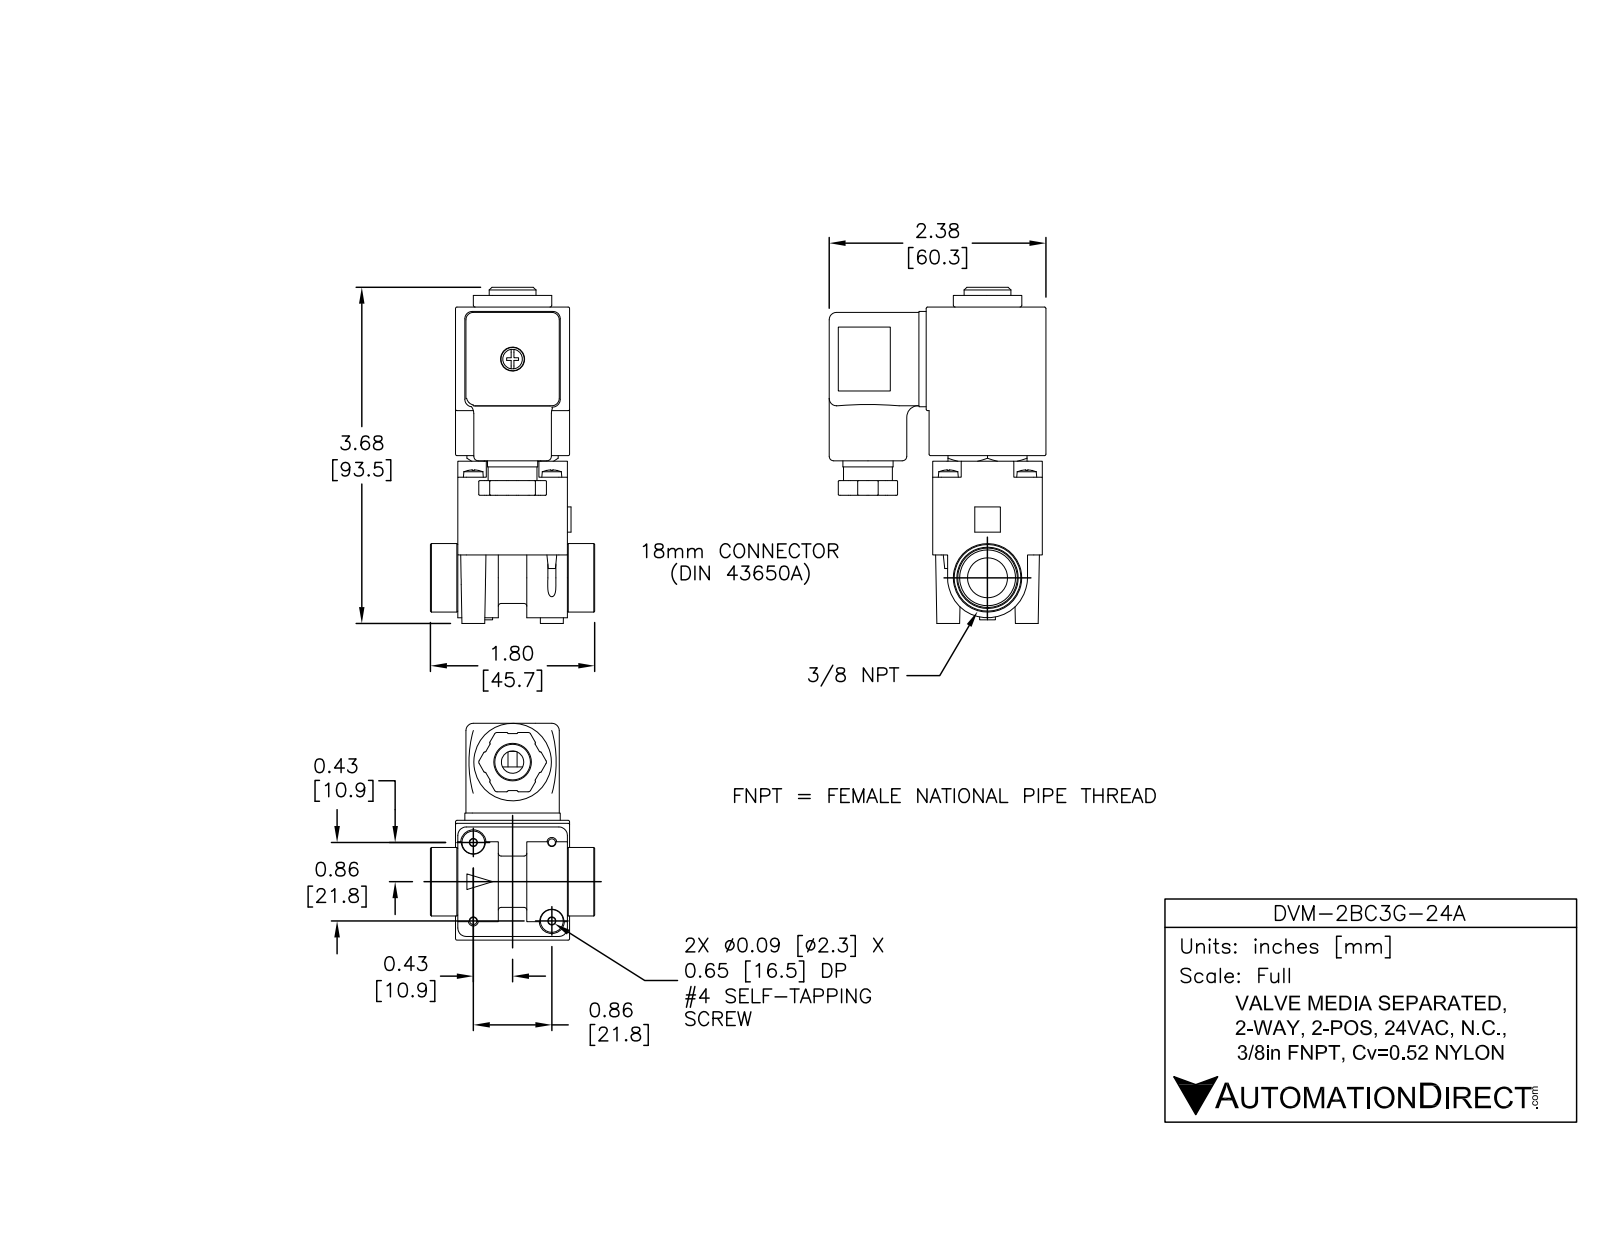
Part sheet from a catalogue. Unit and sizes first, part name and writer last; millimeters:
Units: millimetres
Overall size (bounding box): 93.5 × 60.3 × 45.7
Round holes (diameter × count): ⌀2.8 ×4, ⌀1.5 ×2, ⌀2.3 ×2, ⌀8 ×2, ⌀3 ×1, ⌀4 ×1, ⌀5.2 ×1, ⌀6.2 ×1, ⌀6.4 ×1, ⌀6.7 ×1, ⌀9.9 ×1, ⌀10.2 ×1
Round bosses / shafts (diameter × count): ⌀5.5 ×4, ⌀3.2 ×4, ⌀22.2 ×1, ⌀22.2 ×1, ⌀21.6 ×1, ⌀20.5 ×1, ⌀17.3 ×1, ⌀13.6 ×1
Partial cylindrical surfaces — rounded edges, fillets, slot ends (radius × count): R0.3 ×54, R0.1 ×21, R0.4 ×17, R0.5 ×12, R0.8 ×12, R0.8 ×12, R2 ×12, R1.3 ×8
Main face-to-face distances: 31.8, 30.5, 4.1, 27.6, 1.2, 3.5, 24.7, 31.1, 24.5, 1
Hole centre spacings: 15.4, 15.4, 17.4, 21.8, 21.8, 24.9, 30.9, 37
Volume: 83 820 mm³ · Surface area: 43 890 mm²
Bodies: 14 solids, 1775 faces (895 planar, 351 cylindrical, 529 other)
Part name (STEP PRODUCT): DVM-2BC3G-24A
STEP written by: SolidWorks 2015 (AUTOMOTIVE_DESIGN)
